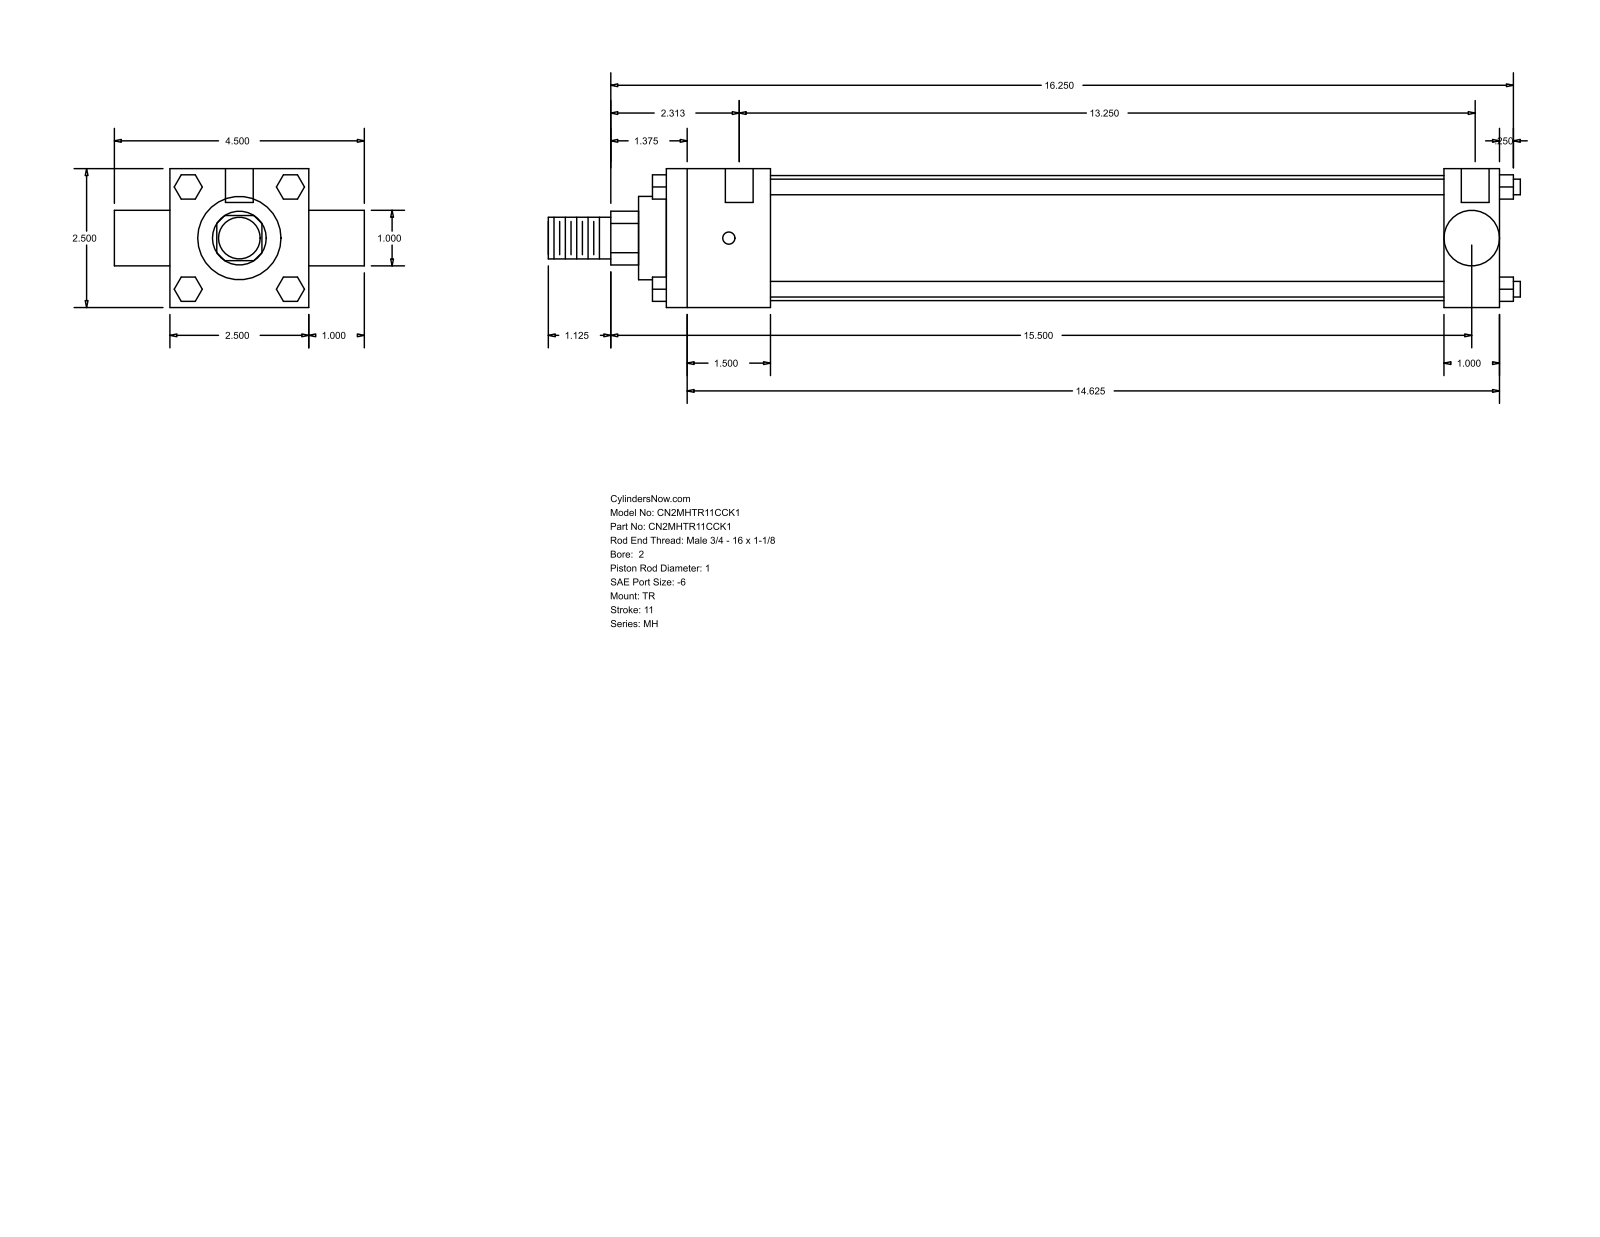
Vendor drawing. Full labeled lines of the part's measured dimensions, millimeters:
Part name (STEP PRODUCT): MH_TR__0200_1
STEP written by: GSSL Pune (CONFIG_CONTROL_DESIGN)
Units: millimetres
Bodies: 0 solids, 120 faces (92 planar, 28 cylindrical, 0 other)
Overall size (bounding box): 444.5 × 114.3 × 63.5
Round holes (diameter × count): ⌀5.56 ×3, ⌀12.7 ×2
Round bosses / shafts (diameter × count): ⌀7.14 ×4, ⌀57.15 ×1, ⌀38.1 ×1, ⌀25.4 ×1, ⌀25.35 ×1, ⌀19.05 ×1
Partial cylindrical surfaces — rounded edges, fillets, slot ends (radius × count): R12.29 ×1
Main face-to-face distances: 63.5, 381, 25.4, 47.63, 355.6, 307.97, 333.37, 88.9, 393.7, 6.35
Hole centre spacings: 3.17, 4.76, 336.55, 339.72, 341.31, 344.48
